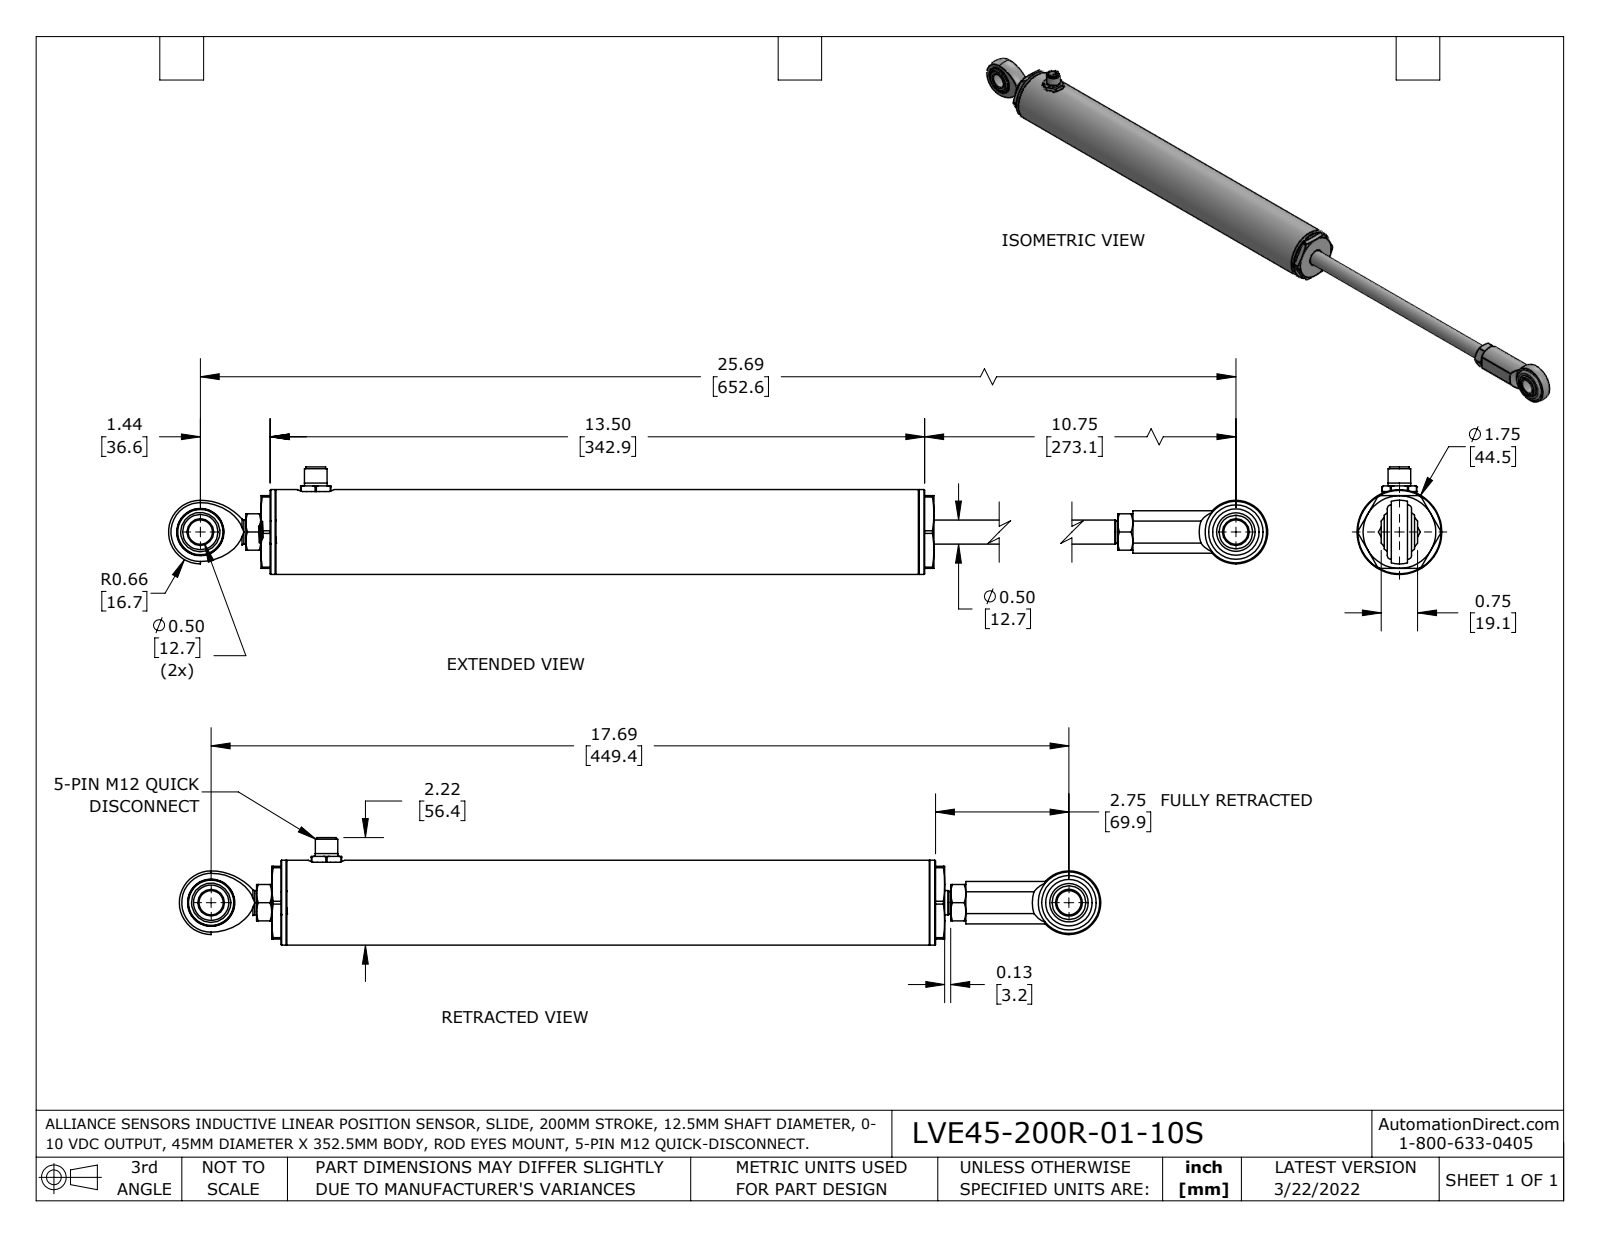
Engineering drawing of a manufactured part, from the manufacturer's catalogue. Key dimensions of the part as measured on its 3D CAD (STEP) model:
Part name (STEP PRODUCT): 3100-0174_9452K116; 3100-0023_9452K91; 3100-0012-YY; 3100-0024_90025K226 (+8 more)
STEP written by: SolidWorks 2021 (AUTOMOTIVE_DESIGN)
Units: inches
Bodies: 23 solids, 873 faces (198 planar, 297 cylindrical, 378 other)
Overall size (bounding box): 27.004 × 2.219 × 1.75
Volume: 17.35 in³ · Surface area: 256.4 in²
Round holes (diameter × count): ⌀0.501 ×3, ⌀0.197 ×1, ⌀0.25 ×1, ⌀0.264 ×1, ⌀0.309 ×1, ⌀0.329 ×1, ⌀0.339 ×1, ⌀0.413 ×1, ⌀0.417 ×1, ⌀0.453 ×1, ⌀0.478 ×1, ⌀0.5 ×1
Round bosses / shafts (diameter × count): ⌀0.031 ×5, ⌀1.75 ×1, ⌀1.625 ×1, ⌀1.562 ×1, ⌀1.531 ×1, ⌀1.5 ×1, ⌀1.47 ×1, ⌀1.384 ×1
Partial cylindrical surfaces — rounded edges, fillets, slot ends (radius × count): R0.325 ×1, R0.354 ×1, R0.378 ×1, R0.38 ×1, R0.438 ×1, R0.85 ×1
Main face-to-face distances: 1.93, 0.5, 0.38, 0.69, 2.62, 11.573, 2.24, 1.55, 11.763, 11.073
Hole centre spacings: 0.5, 25.693
